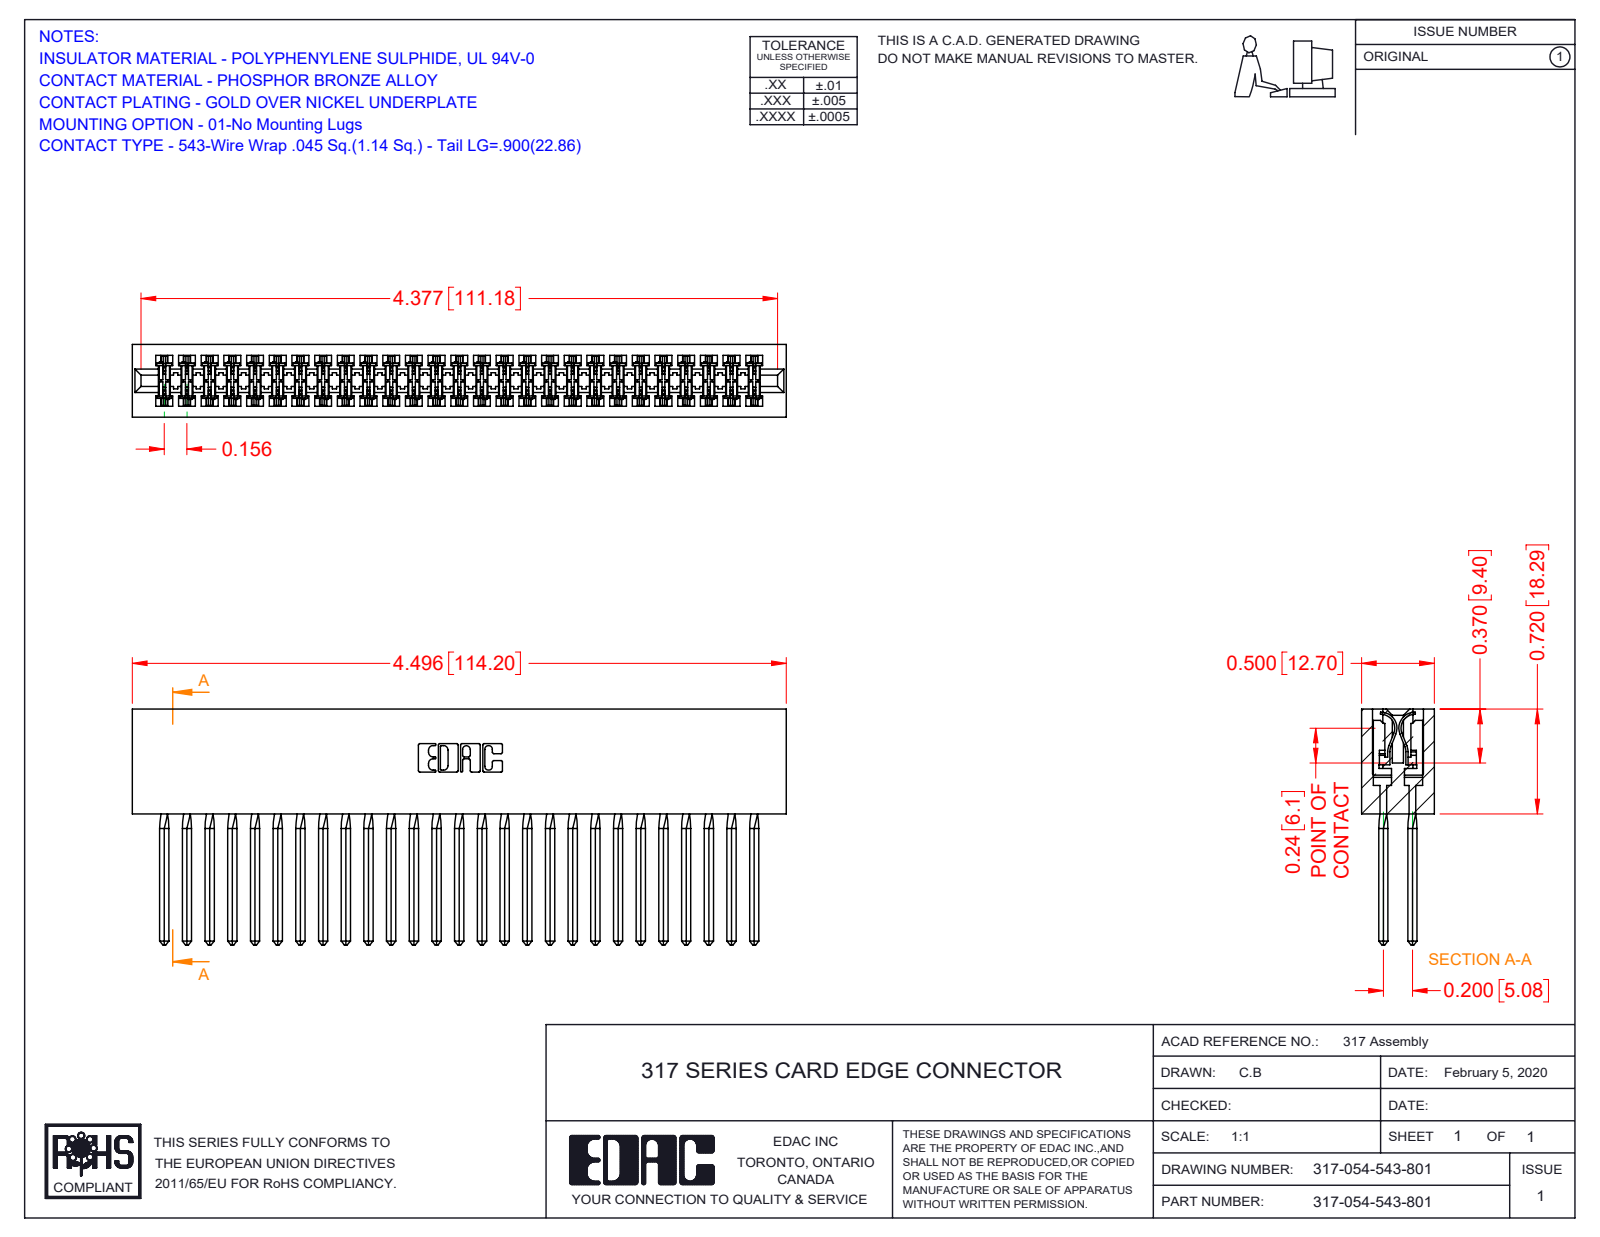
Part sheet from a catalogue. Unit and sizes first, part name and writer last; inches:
Units: inches
Overall size (bounding box): 4.496 × 1.62 × 0.5
Partial cylindrical surfaces — rounded edges, fillets, slot ends (radius × count): R0.015 ×108, R0.01 ×22, R0.007 ×6, R0.031 ×6, R0.026 ×3, R0.095 ×2, R0.1 ×2, R0.11 ×2
Main face-to-face distances: 0.075, 0.5, 0.425, 0.35, 0.11, 0.195, 0.094, 0.72, 0.2, 0.115
Volume: 1.264 in³ · Surface area: 48.24 in²
Bodies: 55 solids, 4896 faces (3992 planar, 688 cylindrical, 216 other)
Part name (STEP PRODUCT): 317-054-543-801; 317 Part_Lugless; 317-290-001_543
STEP written by: SolidWorks 2016 (CONFIG_CONTROL_DESIGN)
